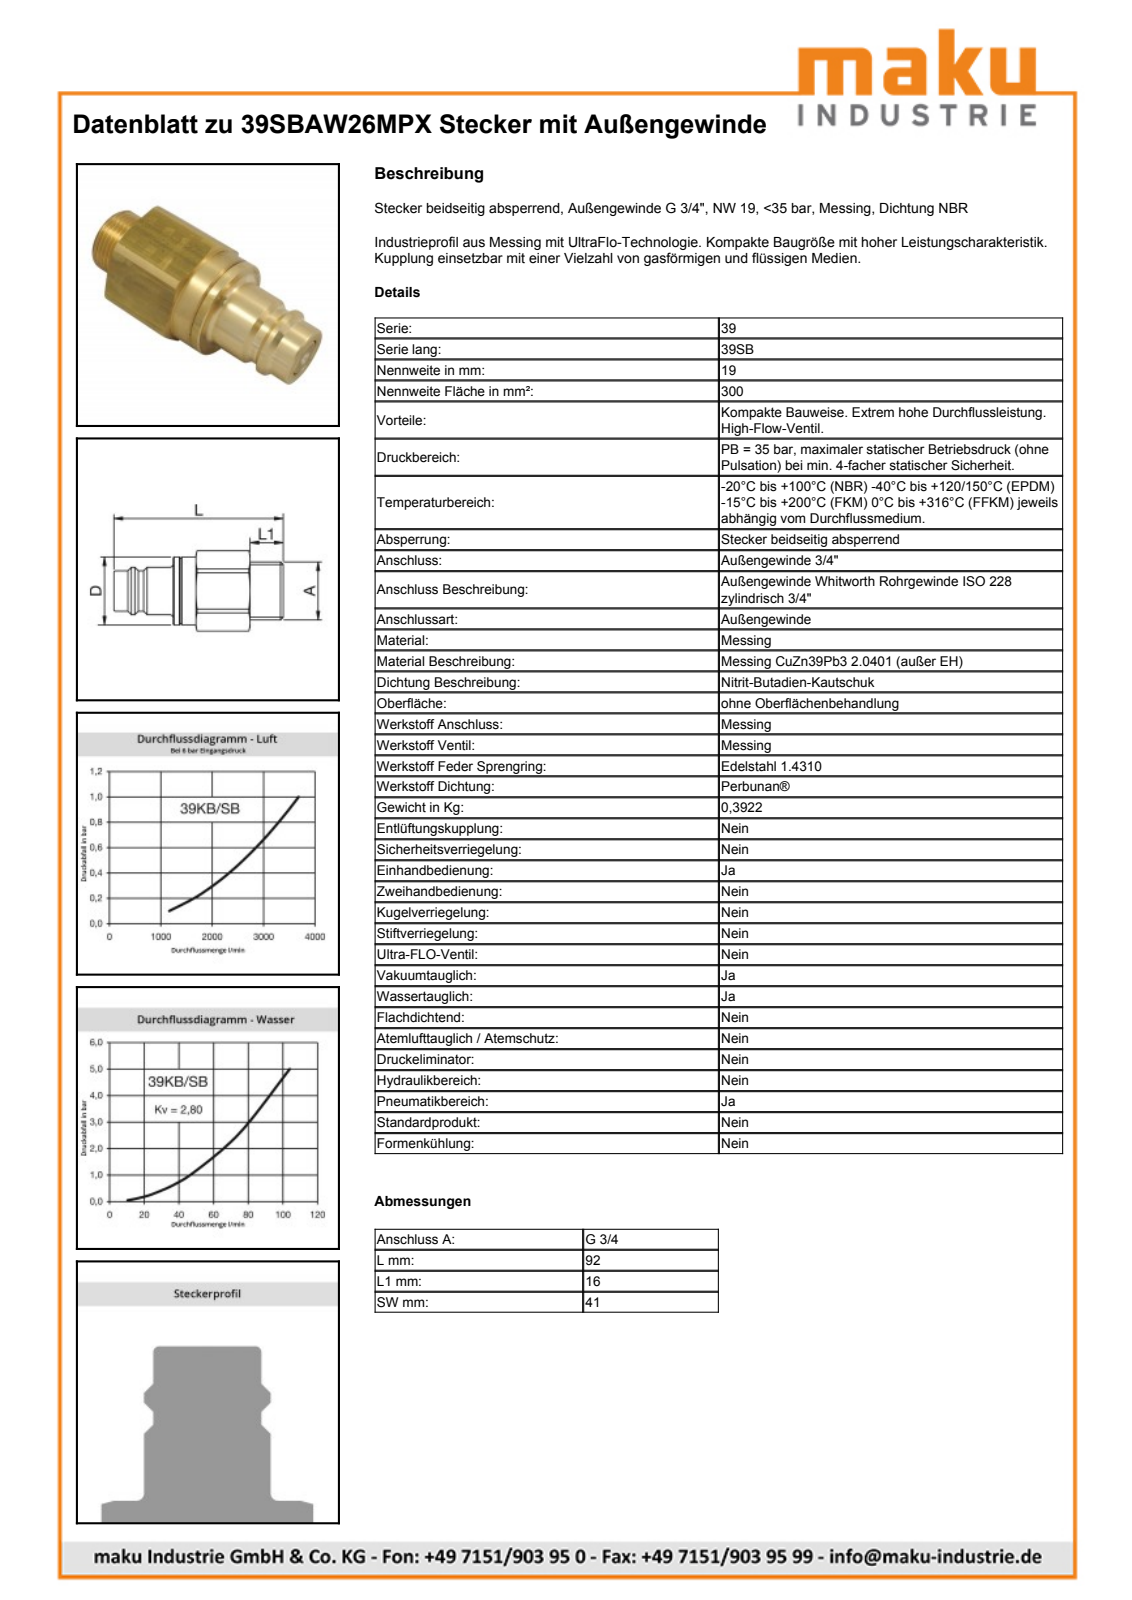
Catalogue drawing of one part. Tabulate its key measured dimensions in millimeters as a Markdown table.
| quantity | value |
| --- | --- |
| part name | D104951 |
| STEP written by | Autodesk Inventor 2013 (AUTOMOTIVE_DESIGN) |
| units | millimeters |
| bodies | 1 solid, 51 faces (13 planar, 15 cylindrical, 23 other) |
| overall size | 94 × 45.95 × 41.96 |
| volume | 86 293 mm³ |
| surface area | 13 519 mm² |
| round holes (diameter × count) | 35 × 1 |
| round bosses / shafts (diameter × count) | 39 × 1, 38.8 × 1, 33 × 1, 27.2 × 1, 26.44 × 1, 23.15 × 1 |
| partial cylindrical surfaces (radius × count) | 22.98 × 1 |
| main face-to-face distances | 40.98, 41, 41.02, 16, 44, 60, 34, 78, 94, 47 |
